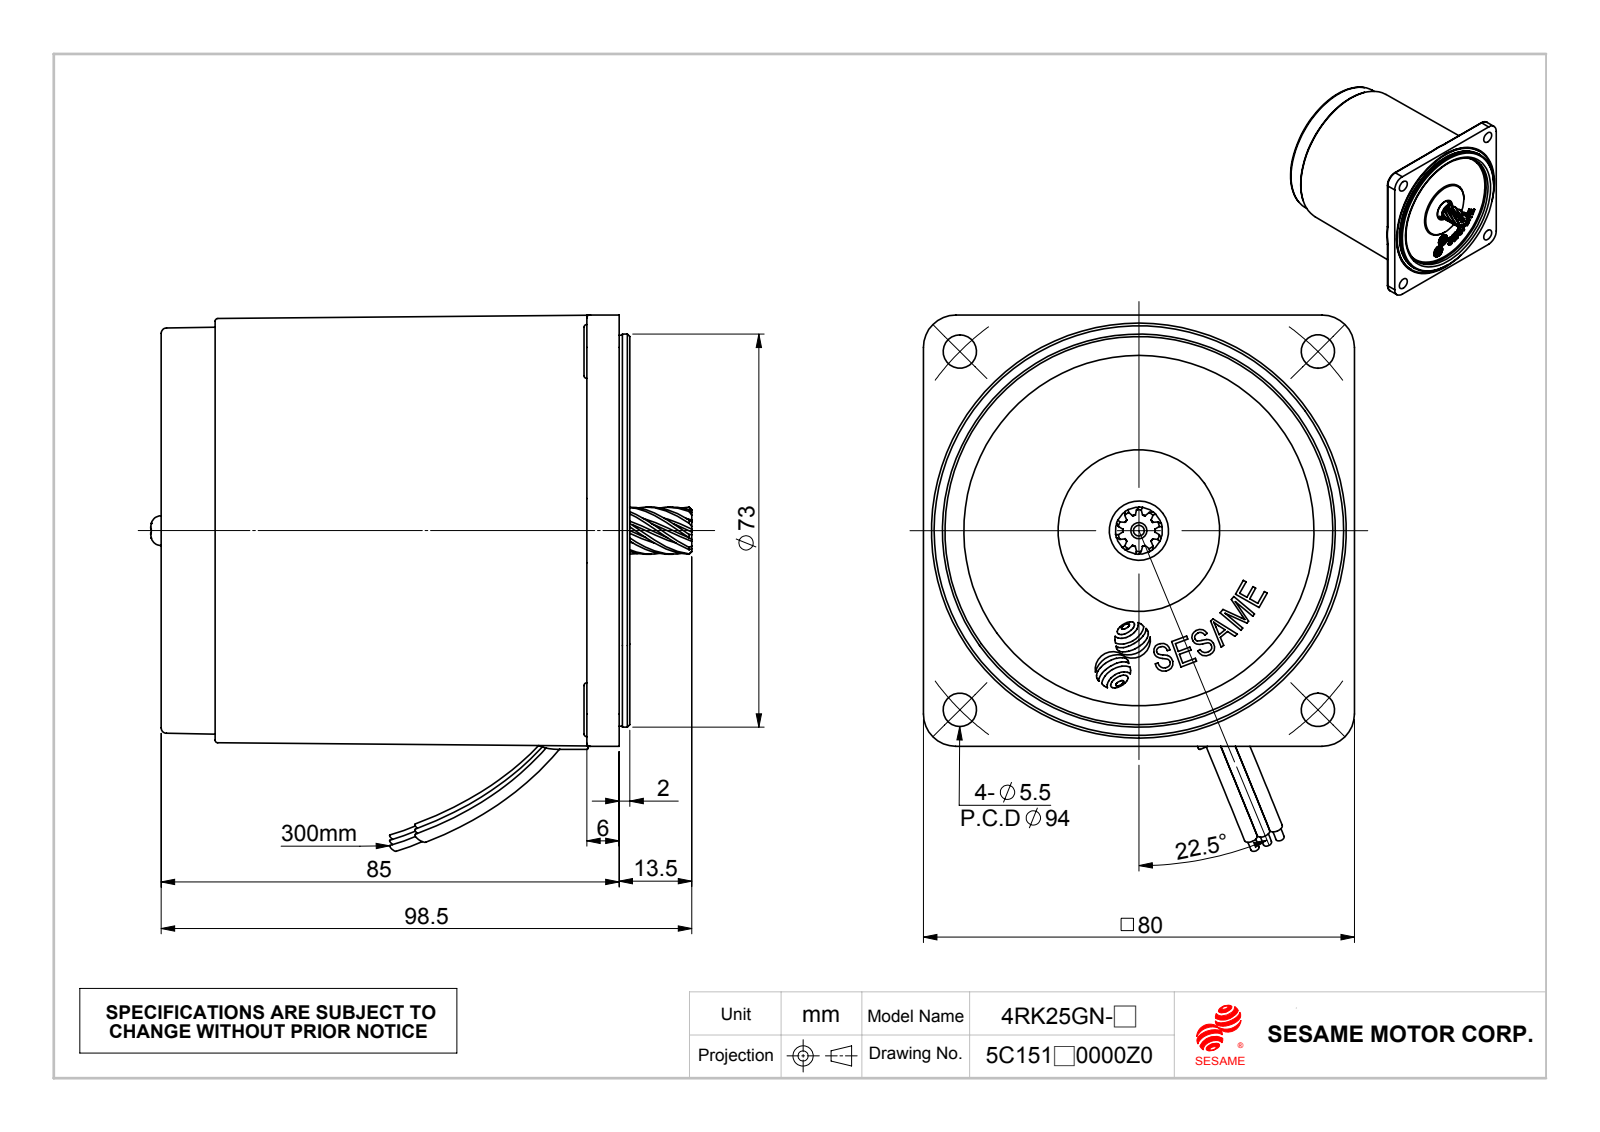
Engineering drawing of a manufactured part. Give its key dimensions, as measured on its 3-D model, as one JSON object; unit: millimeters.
{"part_name": "25GN_Default; C475-C473_C475成品-車工; M425A-RK_成品; 線扣 (+1 more)", "step_written_by": "SolidWorks 2010 (CONFIG_CONTROL_DESIGN)", "units": "millimeters", "bodies": {"solids": 10, "faces": 579, "planar": 175, "cylindrical": 225, "other": 179}, "overall_size": [100.46, 99.5, 80], "volume_mm3": 421790, "surface_area_mm2": 50447, "round_holes": [[6.2, 4], [2.5, 3], [4, 2], [2, 1], [7.2, 1], [9.5, 1], [11, 1], [60, 1], [65, 1], [76, 1]], "round_bosses_or_shafts": [[5.5, 2], [3, 2], [72.93, 1], [72.53, 1], [40, 1], [10, 1], [9.4, 1], [9.3, 1]], "partial_cylinders_radius": [[0.25, 8], [0.3, 8], [0.61, 8], [1.16, 8], [1.29, 8], [2.26, 8], [0.16, 4], [0.45, 4]], "face_to_face_distances": [1, 84, 82.4, 82.5, 0.5, 83.5, 83.4, 0.6, 83, 1.6], "hole_center_spacings": [37.9, 46.99, 58.57, 66.46, 15, 93.99, 30]}
